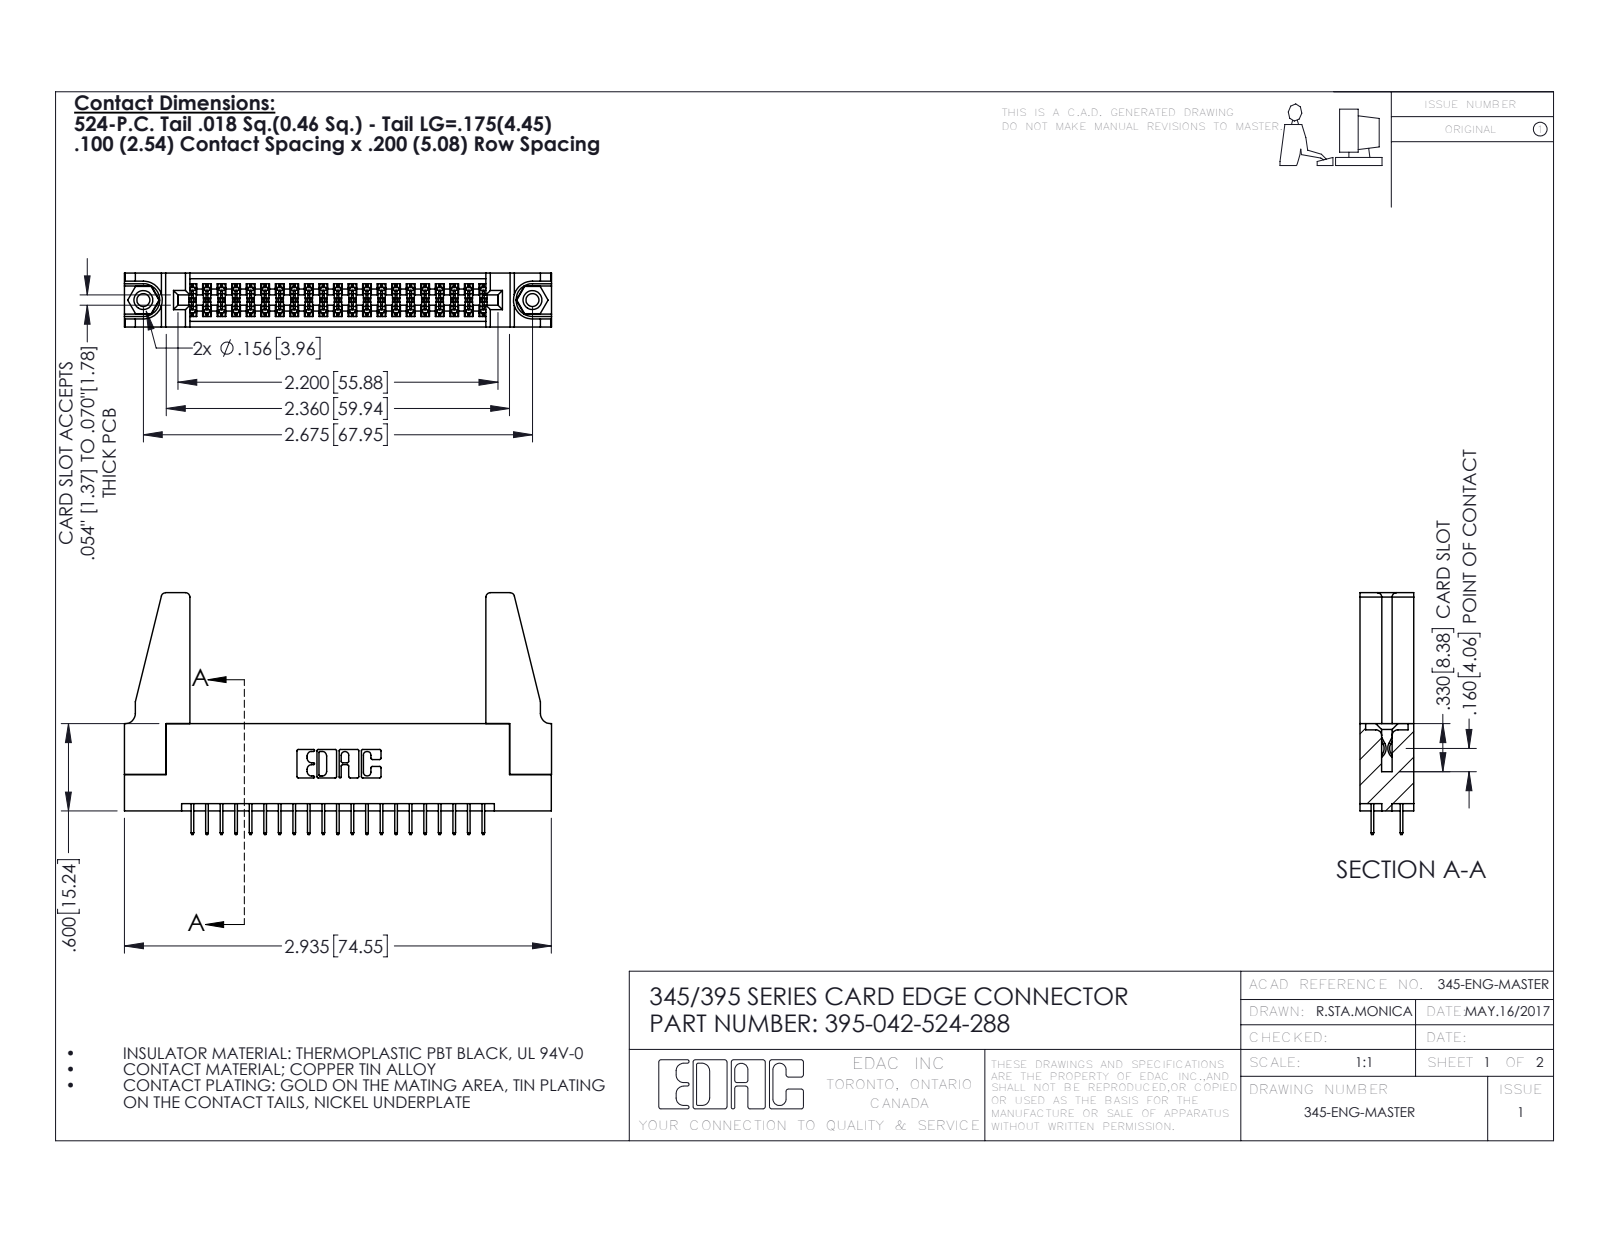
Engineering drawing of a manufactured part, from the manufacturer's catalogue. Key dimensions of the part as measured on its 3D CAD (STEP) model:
Part name (STEP PRODUCT): 395-042-524-288; 345-292-001_345-293-124; 345-220-078_345-220-088; 345 Part_Flush Mounting Lugs - 0.156 Dia-TH (+1 more)
STEP written by: SolidWorks 2016 (CONFIG_CONTROL_DESIGN)
Units: inches
Bodies: 47 solids, 2518 faces (1790 planar, 712 cylindrical, 16 other)
Overall size (bounding box): 2.936 × 1.662 × 0.37
Volume: 0.625 in³ · Surface area: 19.95 in²
Round holes (diameter × count): ⌀0.089 ×2, ⌀0.125 ×2, ⌀0.156 ×2, ⌀0.064 ×1
Round bosses / shafts (diameter × count): ⌀0.155 ×2
Partial cylindrical surfaces — rounded edges, fillets, slot ends (radius × count): R0.006 ×63, R0.01 ×22, R0.03 ×8, R0.007 ×6, R0.031 ×6, R0.026 ×3, R0.014 ×2, R0.019 ×2
Main face-to-face distances: 0.37, 0.072, 0.298, 0.2, 0.098, 0.272, 0.025, 0.225, 0.072, 0.175
Hole centre spacings: 0.27, 2.441, 2.675
